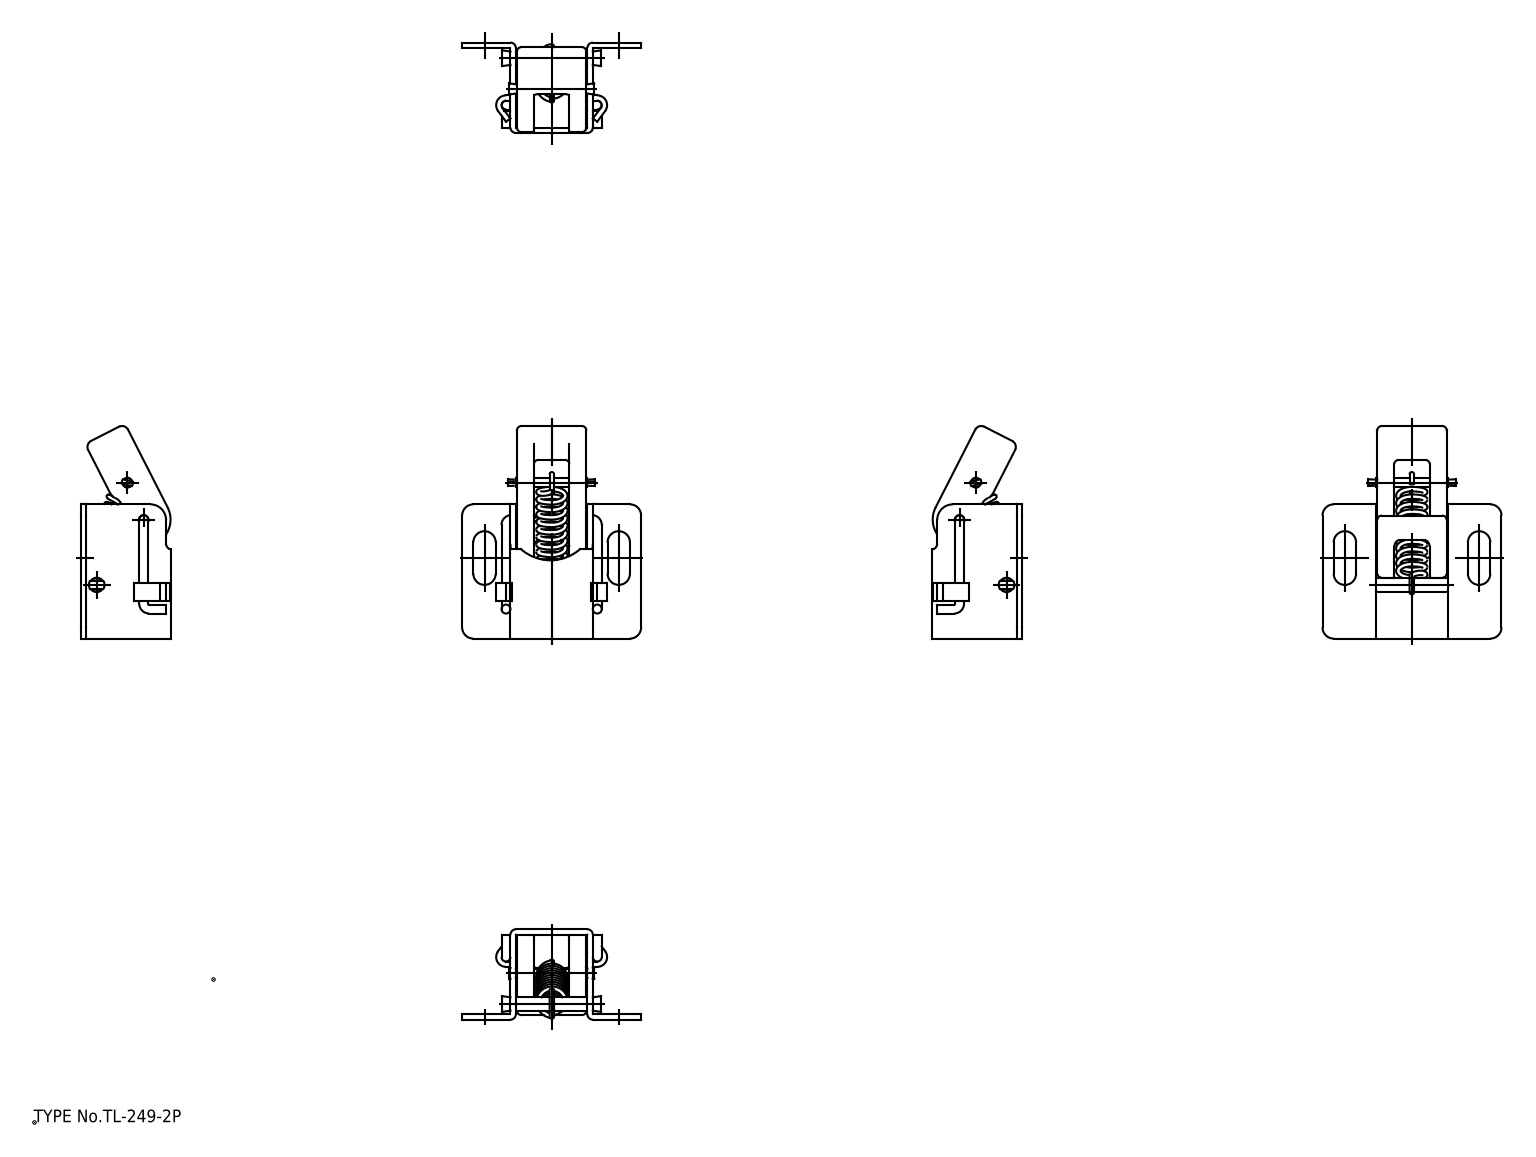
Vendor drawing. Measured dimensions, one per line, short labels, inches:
name: pin_B_mr; pin_B; pin_C; pin_A (+3 more)
written by: spGate 19.8.4 (****-****-****-****) (AUTOMOTIVE_DESIGN)
unit: in
bodies: 6 solids, 318 faces (85 planar, 101 cylindrical, 132 other)
size: 1.871 × 1.575 × 0.795
volume: 0.377 in³; area: 13.04 in²
holes: 3× ⌀0.087, 1× ⌀0.126
bosses: 6× ⌀0.079, 1× ⌀0.118
rounds: 14× R0.012, 14× R0.039, 8× R0.098, 5× R0.059, 4× R0.047, 2× R0.004, 2× R0.028, 2× R0.087
face distances: 0.047, 0.677, 0.15, 0.461, 0.748, 0.63, 0.724, 0.197, 0.508, 0.169
hole spacings: 0.355, 0.359, 0.705, 0.708, 0.939
